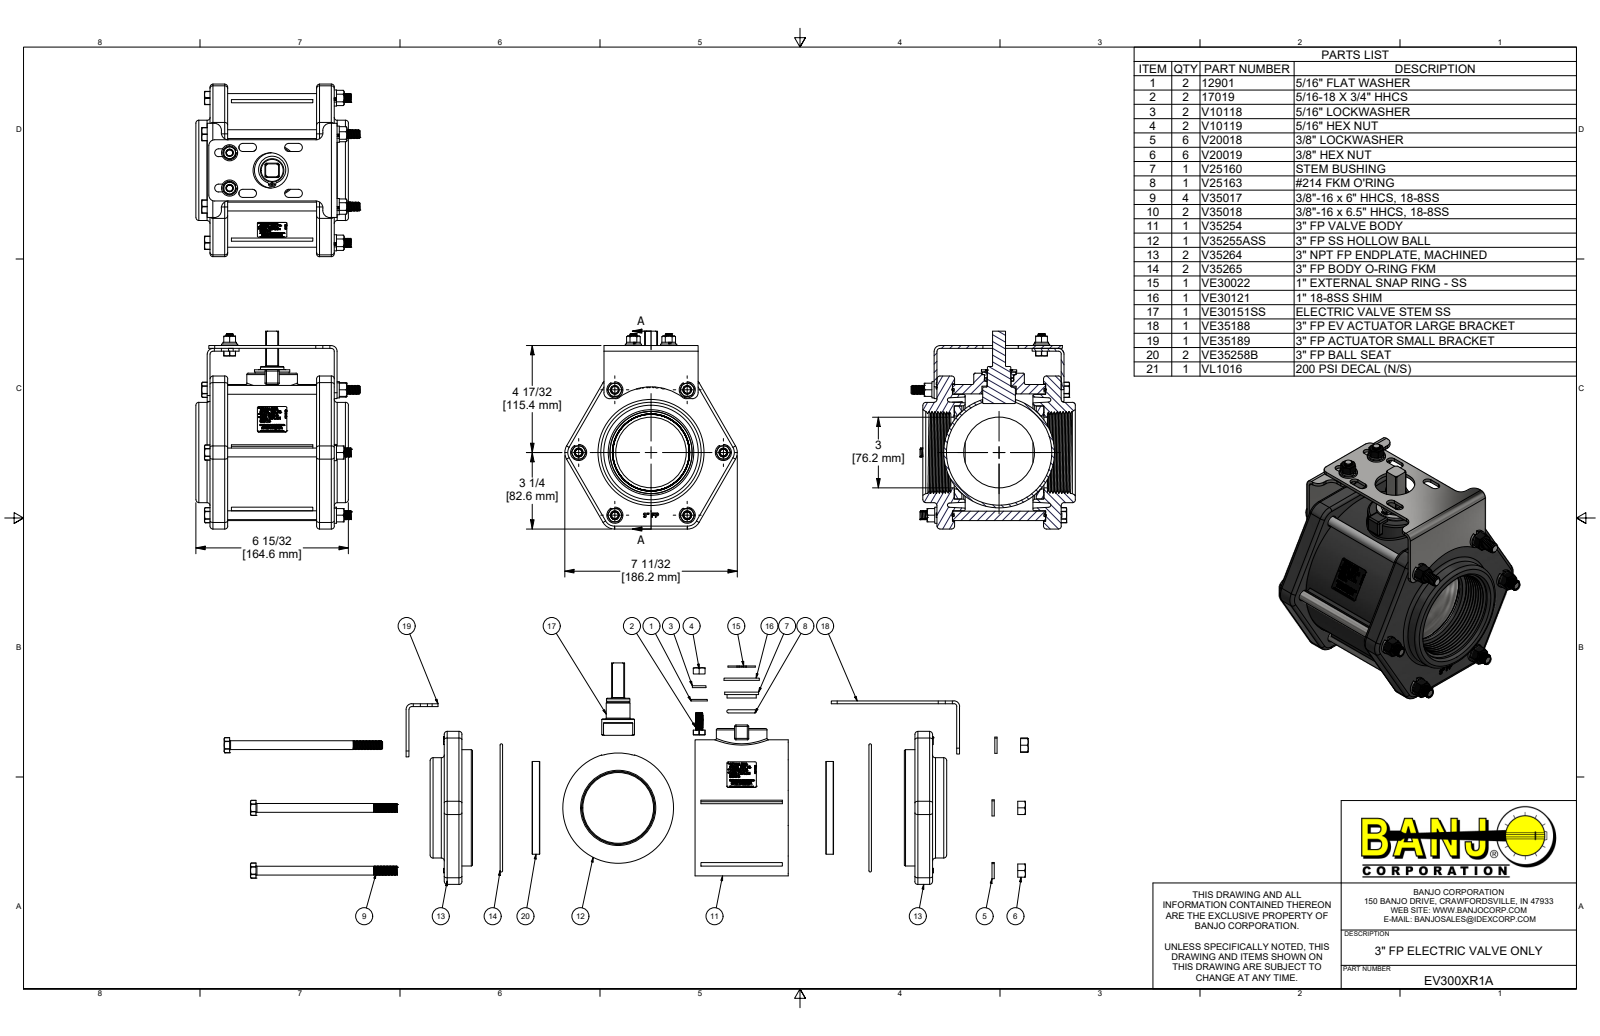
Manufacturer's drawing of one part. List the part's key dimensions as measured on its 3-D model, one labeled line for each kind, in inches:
Part name (STEP PRODUCT): EV300XR1A; V35254; VL1000; V35264 (+8 more)
STEP written by: Autodesk Inventor 2019 (AUTOMOTIVE_DESIGN)
Units: inches
Bodies: 46 solids, 3721 faces (1661 planar, 736 cylindrical, 1324 other)
Overall size (bounding box): 106.072 × 8.405 × 7.331
Volume: 93.65 in³ · Surface area: 1 957 in²
Round holes (diameter × count): ⌀0.171 ×12, ⌀0.307 ×6, ⌀0.385 ×6, ⌀0.44 ×6, ⌀0.282 ×4, ⌀0.076 ×2, ⌀0.252 ×2, ⌀0.322 ×2, ⌀0.344 ×2, ⌀0.375 ×2, ⌀0.41 ×2, ⌀3 ×2
Round bosses / shafts (diameter × count): ⌀0.268 ×26, ⌀0.687 ×6, ⌀0.375 ×6, ⌀0.688 ×2, ⌀0.583 ×2, ⌀0.313 ×2, ⌀0.294 ×2, ⌀5.78 ×1
Partial cylindrical surfaces — rounded edges, fillets, slot ends (radius × count): R0.06 ×28, R0.125 ×24, R0.25 ×12, R0.172 ×8, R0.3 ×8, R0.03 ×6, R0.32 ×6, R0.562 ×6
Main face-to-face distances: 0.12, 5.28, 0.66, 4.62, 0.735, 4.545, 0.075, 3.885, 0.78, 0.855
Hole centre spacings: 2.264, 2.805, 0.813, 3.075, 4.667, 5.418, 5.433, 1.452
